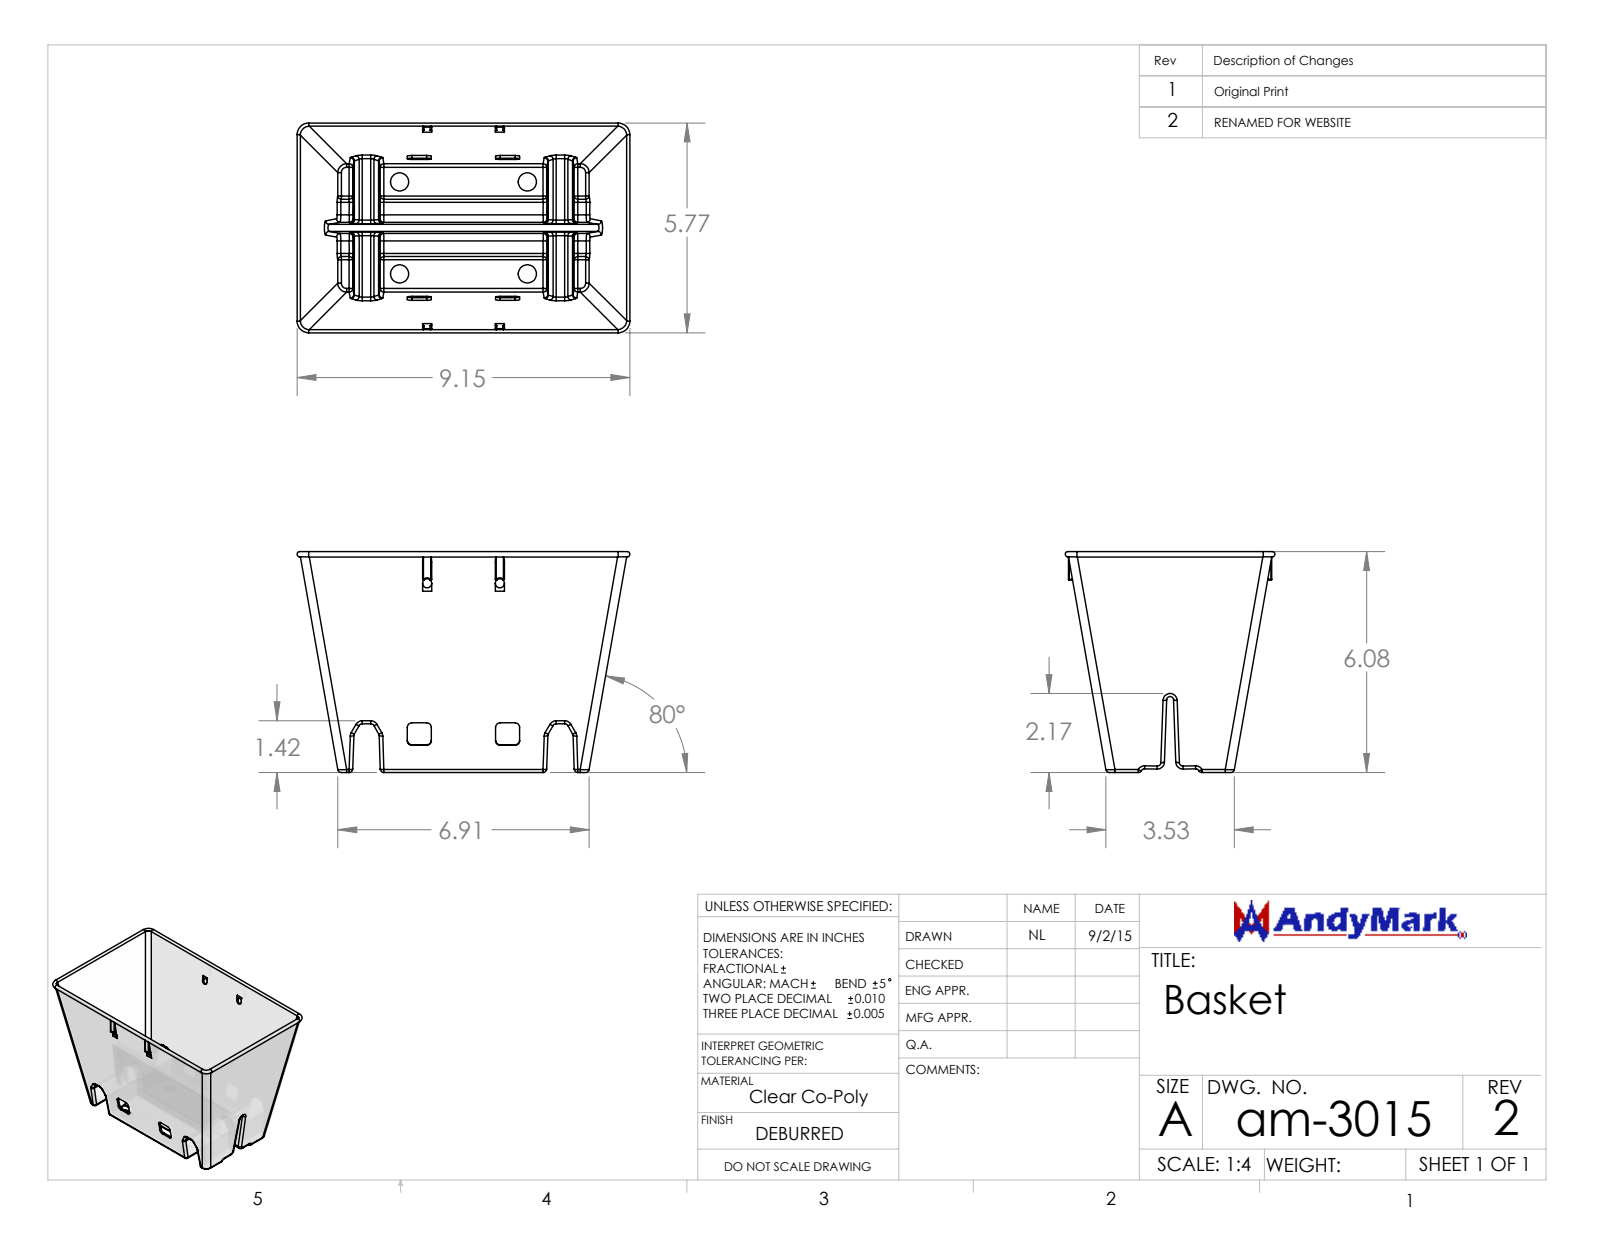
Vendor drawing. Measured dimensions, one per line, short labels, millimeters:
name: am-3015 Basket
written by: SolidWorks 2014 (AUTOMOTIVE_DESIGN)
unit: mm
bodies: 1 solid, 623 faces (128 planar, 281 cylindrical, 214 other)
size: 232.4 × 154.3 × 146.5
volume: 252 900 mm³; area: 264 800 mm²
holes: 4× ⌀12.7, 2× ⌀6.4
rounds: 74× R0.6, 70× R2.5, 18× R3.2, 12× R4.4, 4× R1.9, 4× R6.4, 3× R2.4, 3× R4.3
face distances: 1.9, 1.9, 135.3, 137.2, 133.4, 133.4, 135.3, 117.3, 119.2, 115.4
hole spacings: 64.2, 89.3, 110, 50.8
